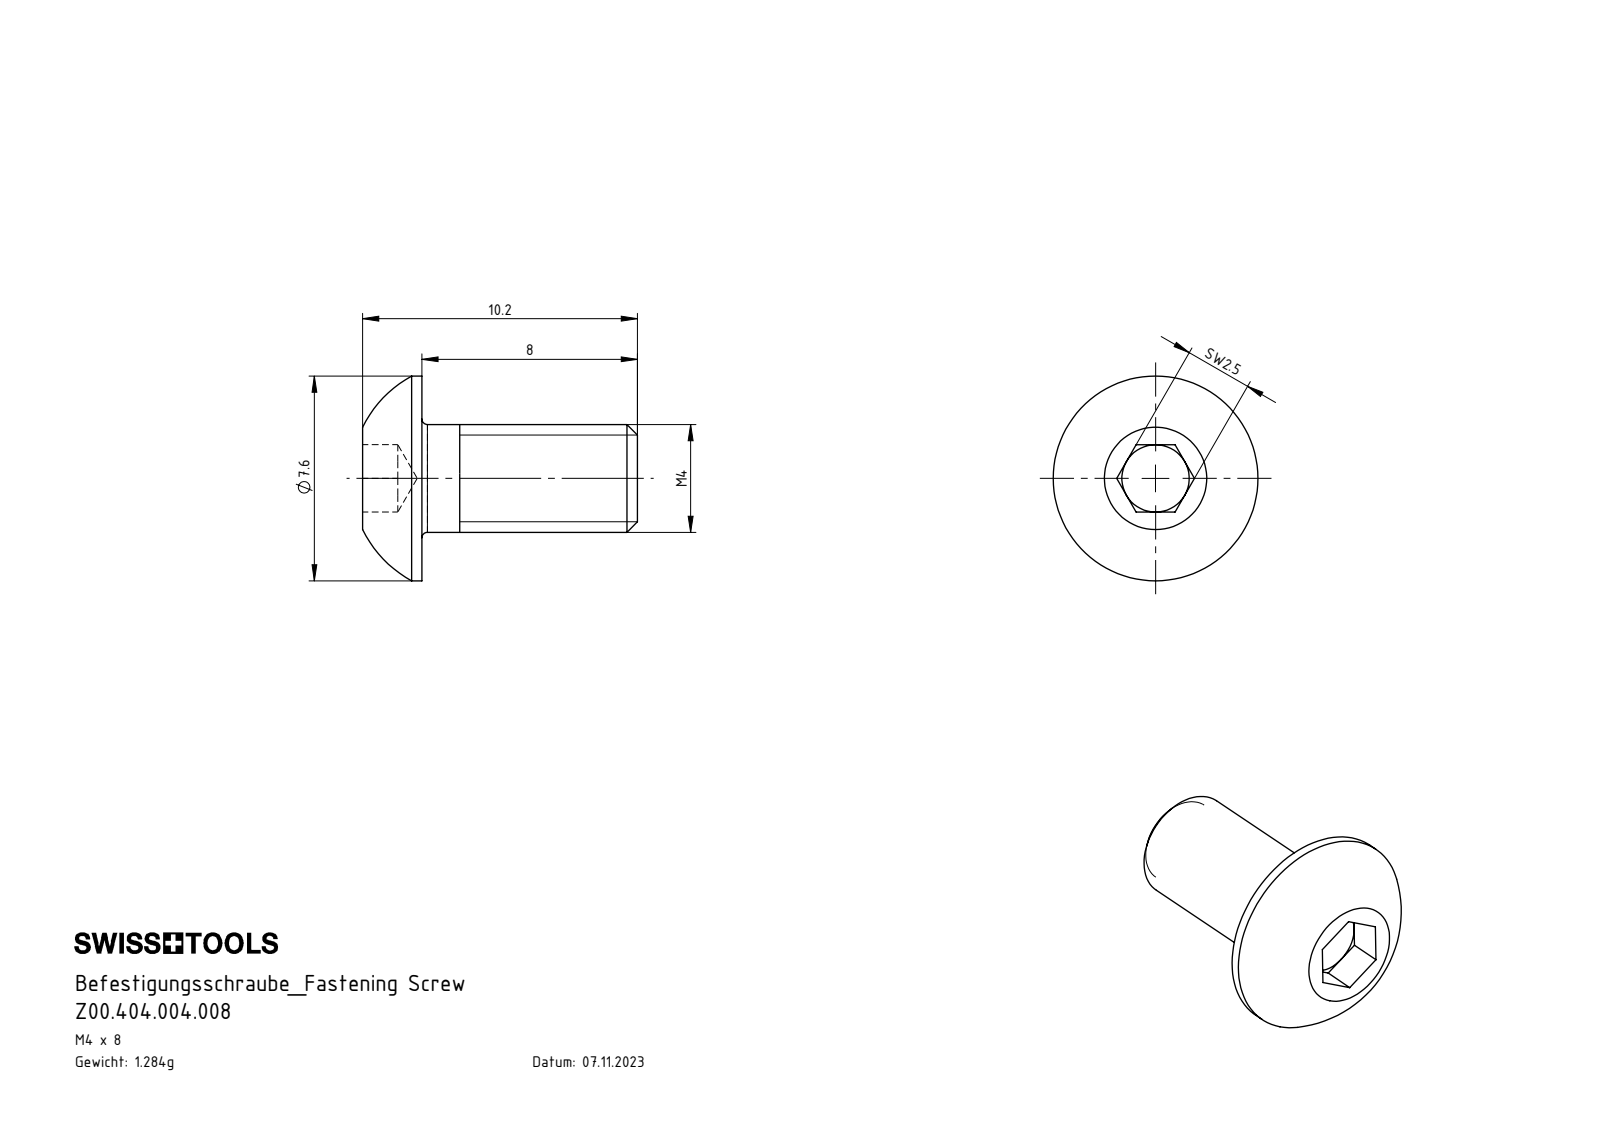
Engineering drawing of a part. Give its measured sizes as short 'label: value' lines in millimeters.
name: Z00.404.004.008
written by: SolidWorks 2022 (AUTOMOTIVE_DESIGN)
unit: mm
bodies: 1 solid, 27 faces (15 planar, 4 cylindrical, 8 other)
size: 10.2 × 7.6 × 7.6
volume: 164 mm³; area: 224 mm²
bosses: 1× ⌀7.6, 1× ⌀4
face distances: 8, 2.2, 10.2, 2.5, 1.3, 0.9, 8.9
